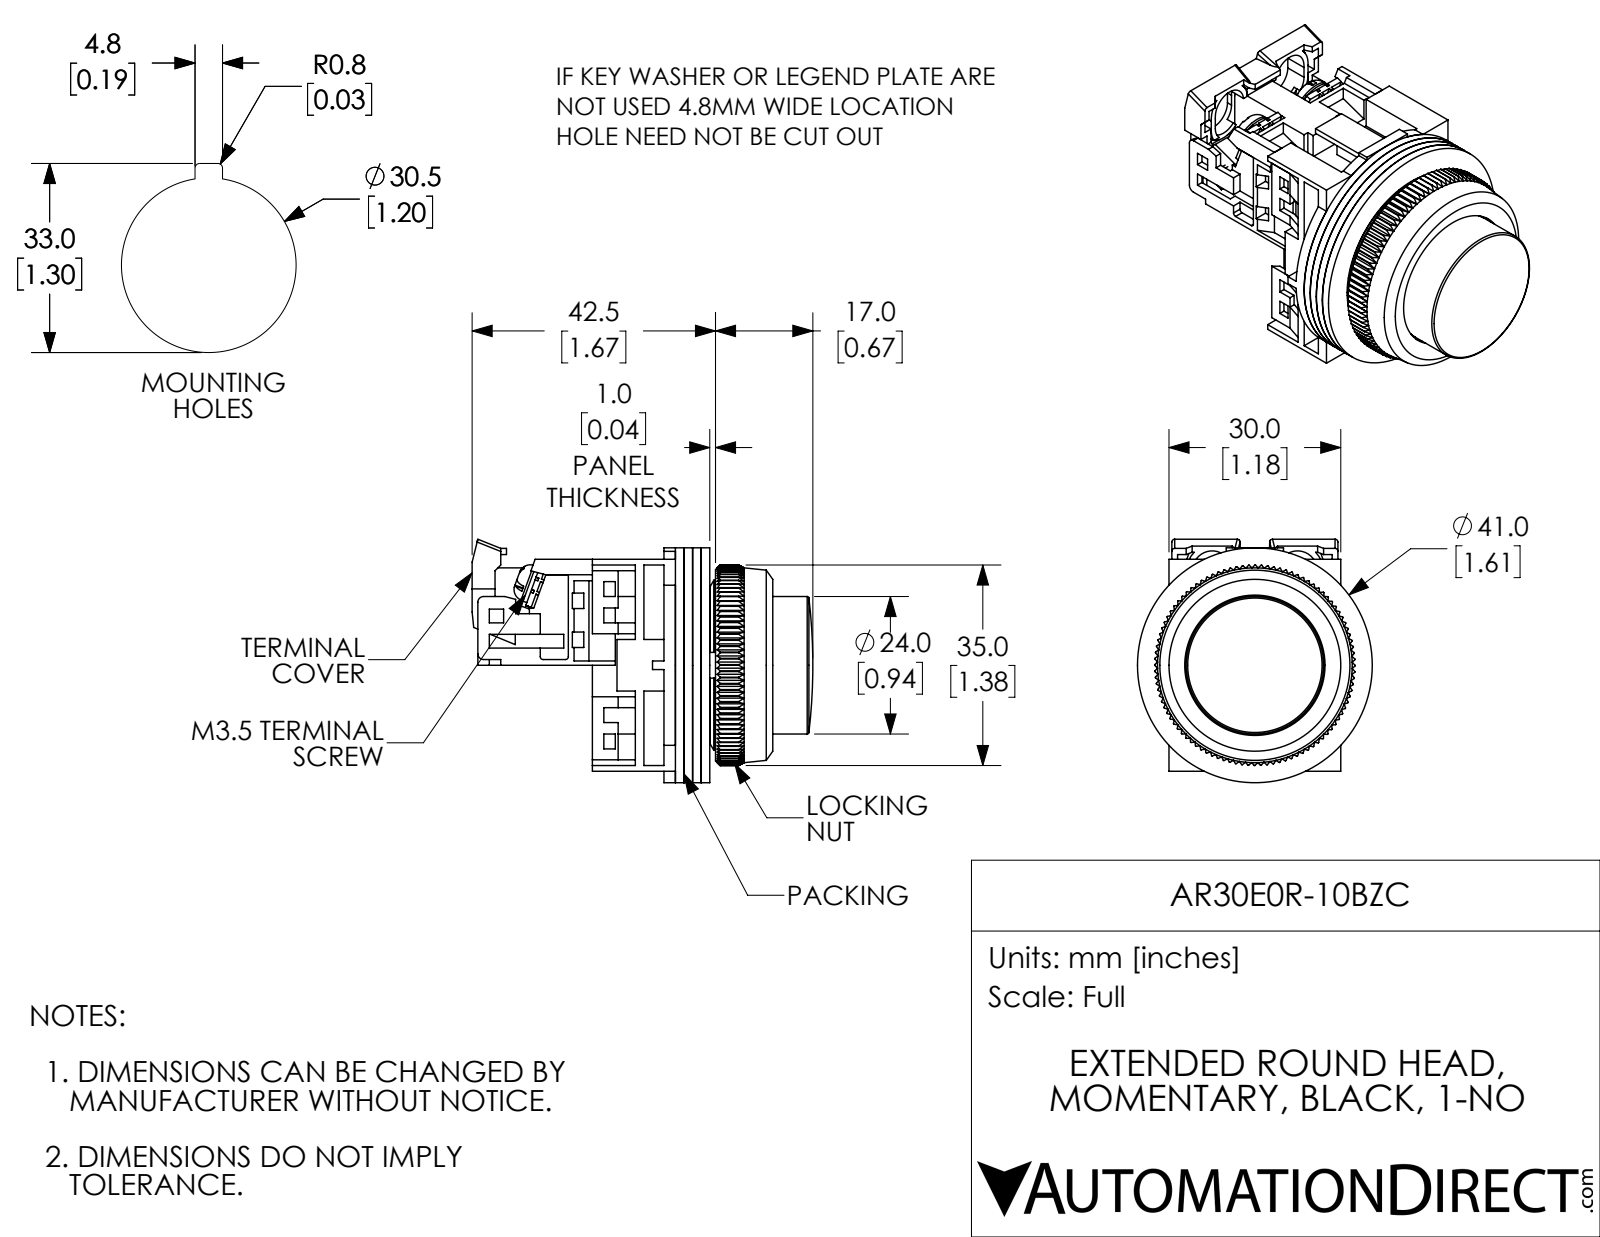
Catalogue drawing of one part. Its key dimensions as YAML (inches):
part_name: "AR30E0R-10BZC"
step_written_by: "SolidWorks 2017 (AUTOMOTIVE_DESIGN)"
units: inches
bodies: {solids: 16, faces: 1234, planar: 775, cylindrical: 249, other: 210}
overall_size: [2.342, 1.673, 1.614]
volume: 1.642
surface_area: 48.85
round_holes:
  - {diameter: 0.138, count: 4}
  - {diameter: 0.142, count: 2}
  - {diameter: 0.118, count: 1}
  - {diameter: 0.472, count: 1}
  - {diameter: 0.709, count: 1}
  - {diameter: 0.787, count: 1}
  - {diameter: 0.945, count: 1}
  - {diameter: 0.965, count: 1}
  - {diameter: 1.122, count: 1}
  - {diameter: 1.252, count: 1}
round_bosses_or_shafts:
  - {diameter: 0.26, count: 2}
  - {diameter: 0.138, count: 2}
  - {diameter: 1.614, count: 1}
  - {diameter: 1.181, count: 1}
  - {diameter: 0.866, count: 1}
  - {diameter: 0.551, count: 1}
partial_cylinders:
  - {radius: 0.059, count: 8}
  - {radius: 0.02, count: 6}
  - {radius: 0.039, count: 2}
  - {radius: 0.138, count: 2}
  - {radius: 0.177, count: 2}
  - {radius: 0.118, count: 1}
  - {radius: 0.398, count: 1}
  - {radius: 0.449, count: 1}
face_to_face_distances: [0.059, 0.118, 0.177, 0.039, 0.197, 0.079, 0.276, 0.689, 0.728, 0.602]
hole_center_spacings: [0.579, 0.61]
